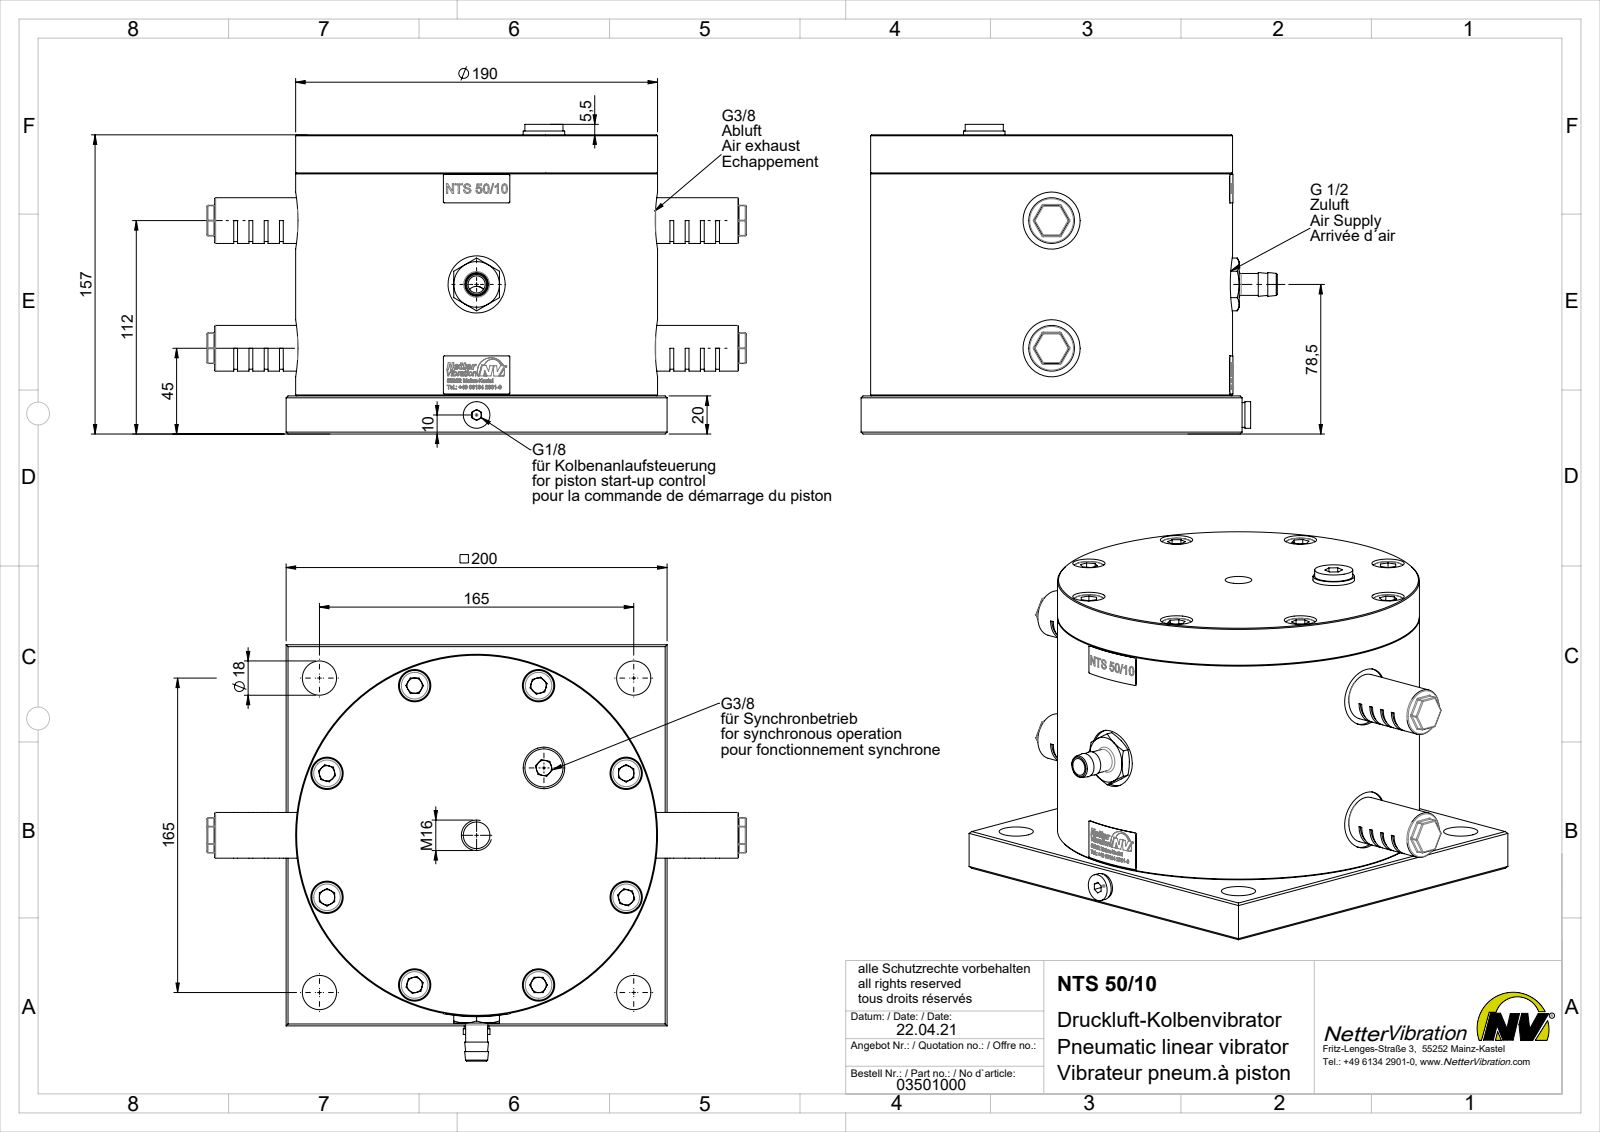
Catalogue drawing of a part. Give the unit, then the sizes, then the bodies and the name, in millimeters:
Units: millimetres
Overall size (bounding box): 279 × 218.5 × 162.5
Round holes (diameter × count): ⌀10.5 ×8, ⌀11 ×8, ⌀17 ×8, ⌀18 ×4, ⌀14.95 ×3, ⌀30 ×3, ⌀6 ×1, ⌀8.57 ×1, ⌀9 ×1, ⌀9.6 ×1, ⌀14 ×1, ⌀15 ×1
Round bosses / shafts (diameter × count): ⌀16 ×8, ⌀10 ×8, ⌀24 ×2, ⌀16.66 ×2, ⌀190 ×1, ⌀21.8 ×1, ⌀20.96 ×1, ⌀20 ×1
Partial cylindrical surfaces — rounded edges, fillets, slot ends (radius × count): R0.5 ×72, R11 ×2, R95.2 ×1
Main face-to-face distances: 1, 156, 157, 19, 20, 137, 200, 6.5, 193.5, 187
Hole centre spacings: 50.13, 85, 115.1, 120.21, 157.06, 168.61, 197.9, 65.05
Volume: 4 707 000 mm³ · Surface area: 239 404 mm²
Bodies: 6 solids, 1197 faces (412 planar, 493 cylindrical, 292 other)
Part name (STEP PRODUCT): NTS 50-10 Kolbenvibrator #03501000
STEP written by: SolidWorks 2010 (AUTOMOTIVE_DESIGN)
